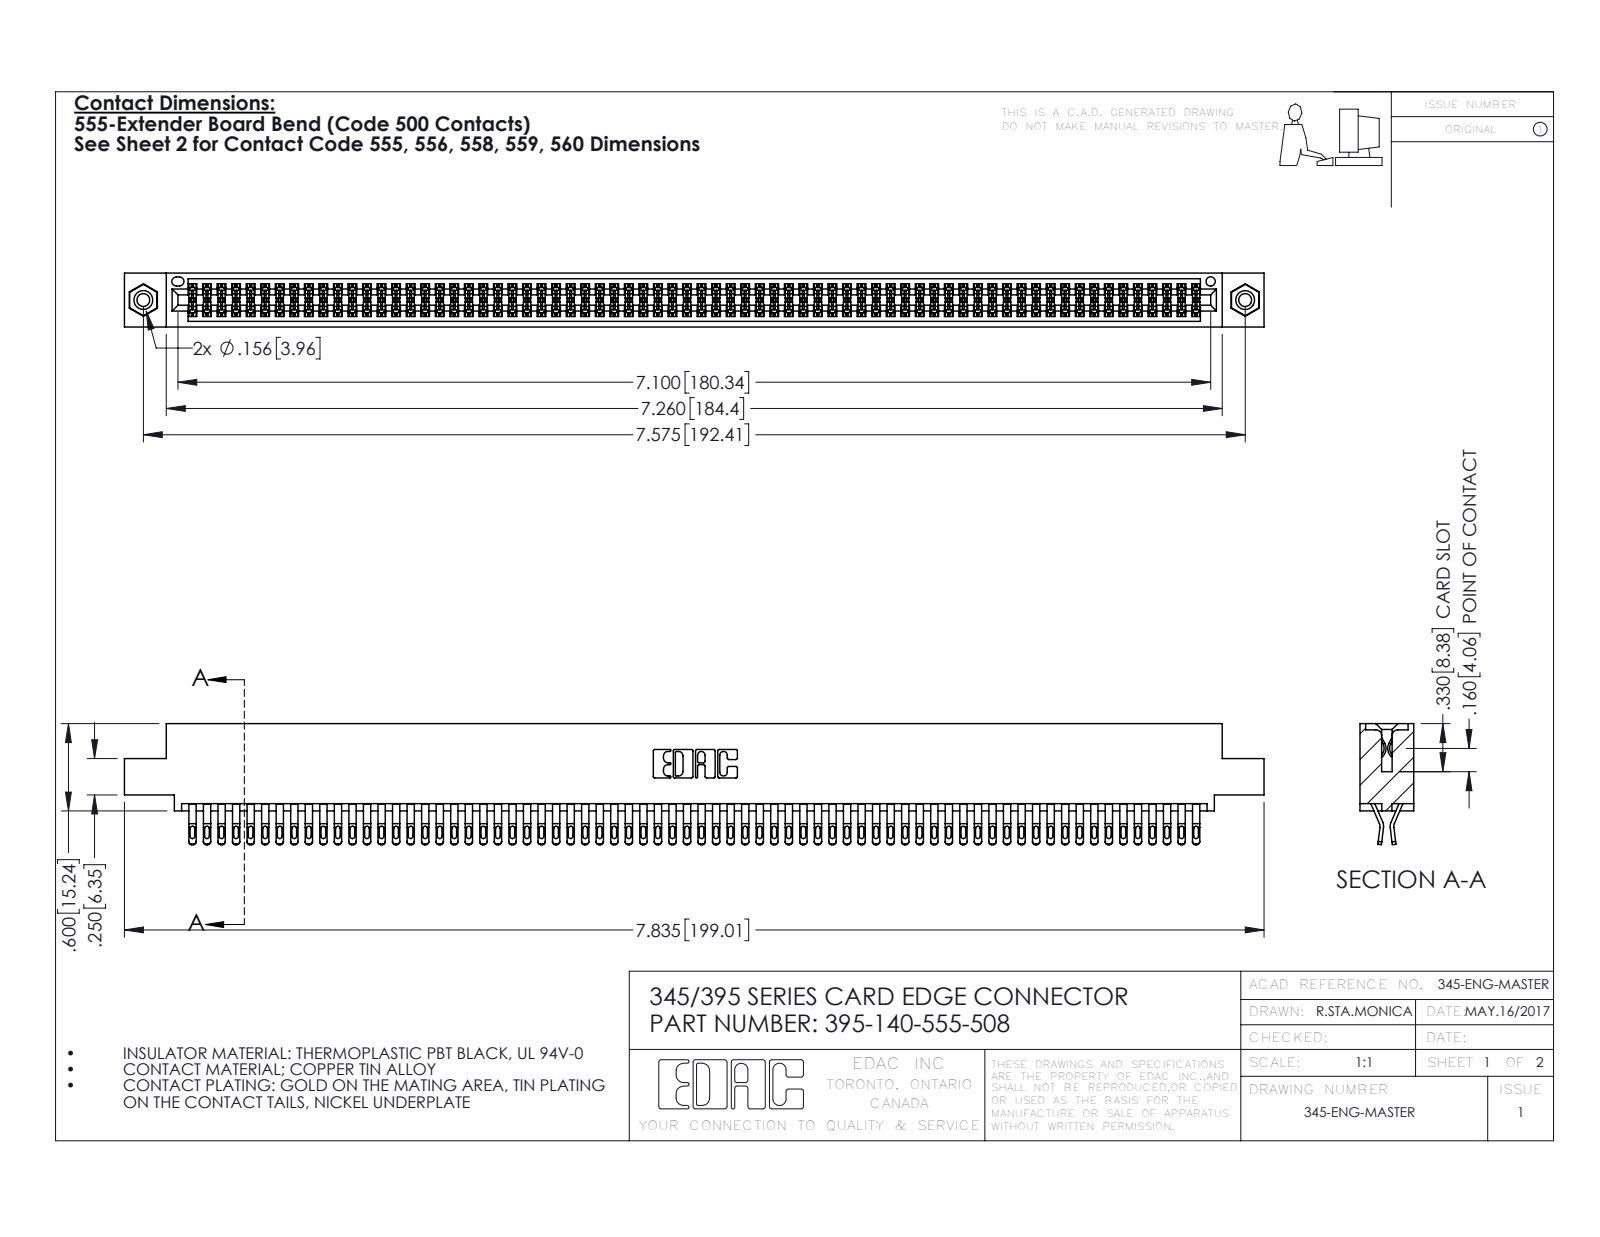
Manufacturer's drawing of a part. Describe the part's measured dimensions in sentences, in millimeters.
The part is named "345-292-001_555 Tail; 345-250-001_345-250-003-102; 345 Part_0.110 Offset - 0.156 Dia-TI; 395-140-555-508". Its 3-D file was written by "SolidWorks 2016 (CONFIG_CONTROL_DESIGN)". It is 143 solids with 8030 faces: 4456 planar, 3558 cylindrical and 16 other. Overall it measures 199 by 21.1 by 9.4 millimeters. Its volume is 19 910 cubic millimeters and its surface area 31 500 square millimeters. Round holes: 2 of diameter 2.3, 2 of diameter 3.2, 2 of diameter 4, 1 of diameter 1.6. Round bosses or shafts: 2 of diameter 3.9. Partial cylindrical surfaces (rounded edges, fillets, slot ends): 350 of radius 0.4, 280 of radius 0.5, 210 of radius 0.2, 22 of radius 0.3, 6 of radius 0.2, 6 of radius 0.8, 3 of radius 0.7, 2 of radius 0.3. The main face-to-face distances are 1.8, 7.6, 0.6, 9.4, 5.1, 2.5, 6.9, 5.7, 4.4, 3.8. The hole center spacings are 6.9, 186.4, 192.4.
